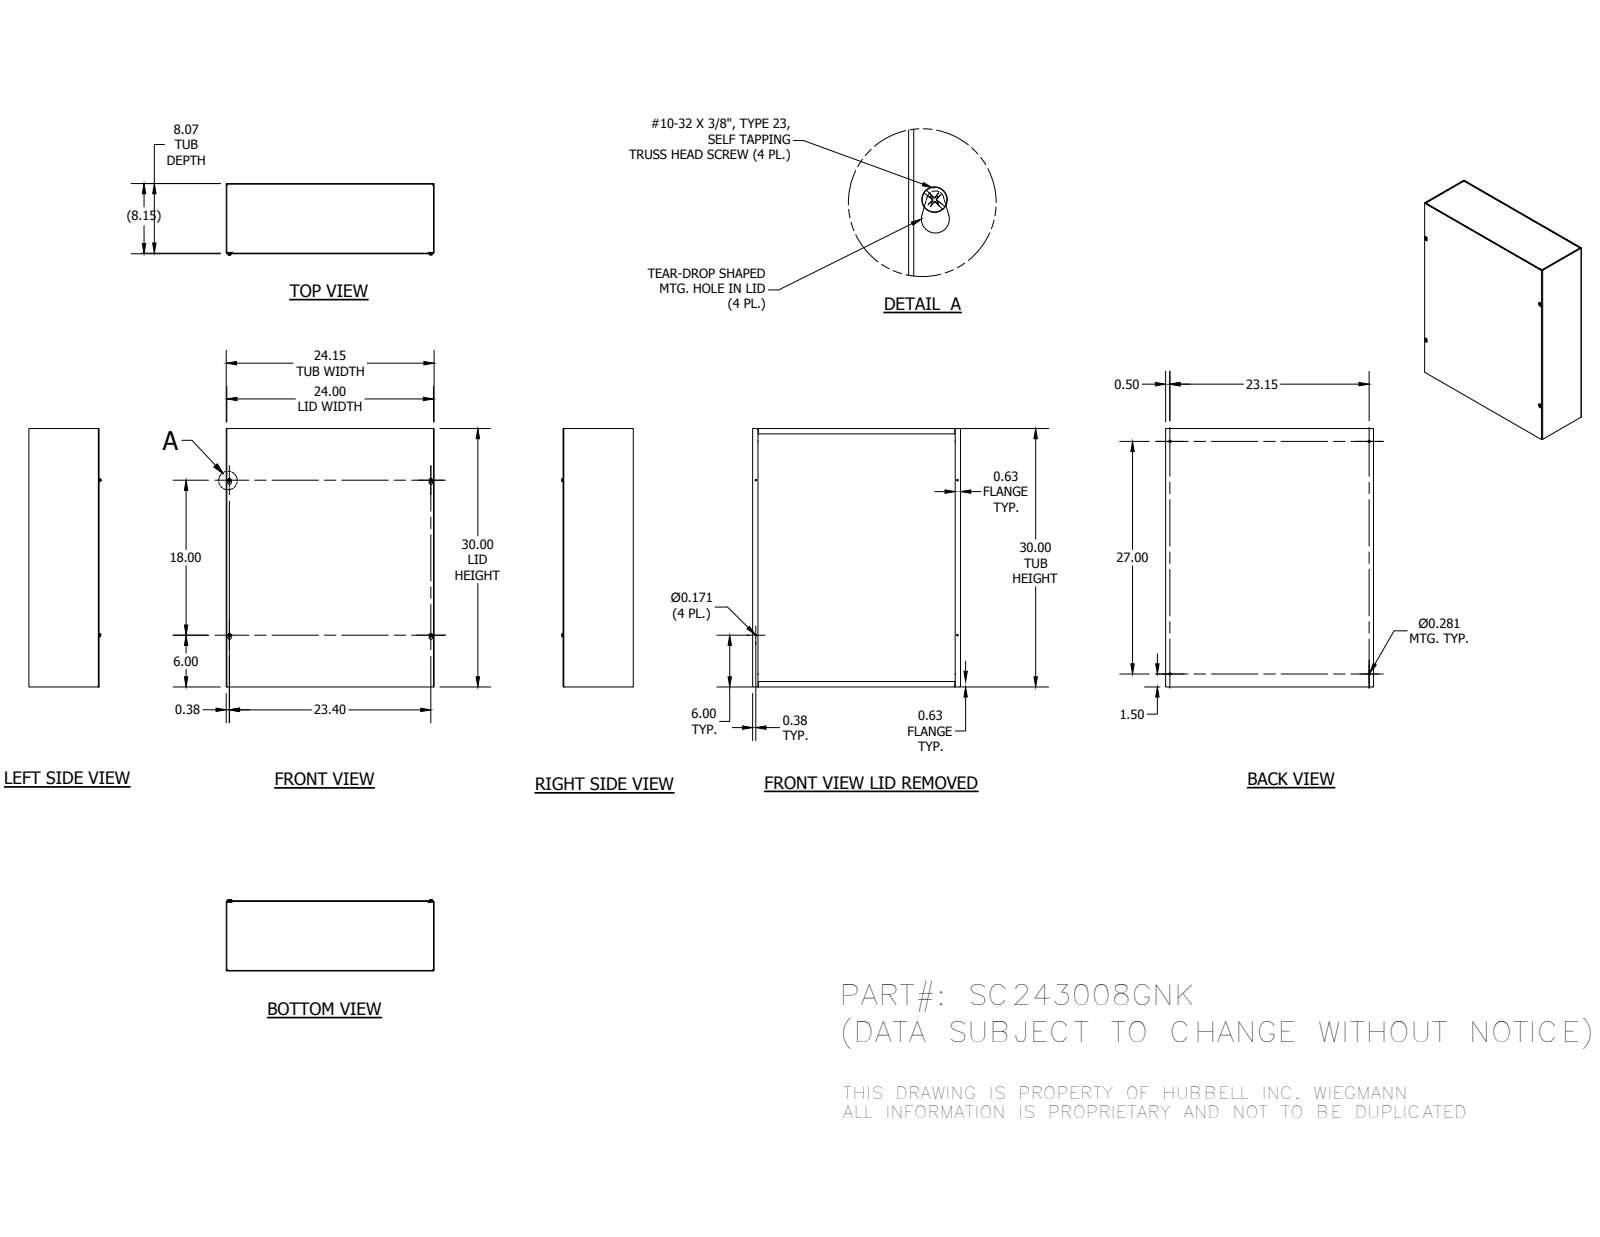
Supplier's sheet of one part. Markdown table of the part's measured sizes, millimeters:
| quantity | value |
| --- | --- |
| part name | SC243008GNKBLR; SC2408GNKTB; SC2430GLPA; 37214 (+1 more) |
| STEP written by | Autodesk Inventor 2014 (AUTOMOTIVE_DESIGN) |
| units | millimeters |
| bodies | 8 solids, 320 faces (192 planar, 44 cylindrical, 84 other) |
| overall size | 762 × 613.36 × 210.31 |
| volume | 2 916 000 mm³ |
| surface area | 3 122 000 mm² |
| round holes (diameter × count) | 4.34 × 4, 7.14 × 4 |
| round bosses / shafts (diameter × count) | 4.83 × 4 |
| partial cylindrical surfaces (radius × count) | 0.4 × 12, 2.28 × 12, 3.17 × 4, 5.16 × 4 |
| main face-to-face distances | 1.88, 205.08, 203.2, 206.96, 611.48, 760.12, 609.6, 613.36, 762, 758.24 |
| hole center spacings | 114.34, 571.51, 602.08, 822.22, 457.2, 587.96, 594.3, 685.8 |
